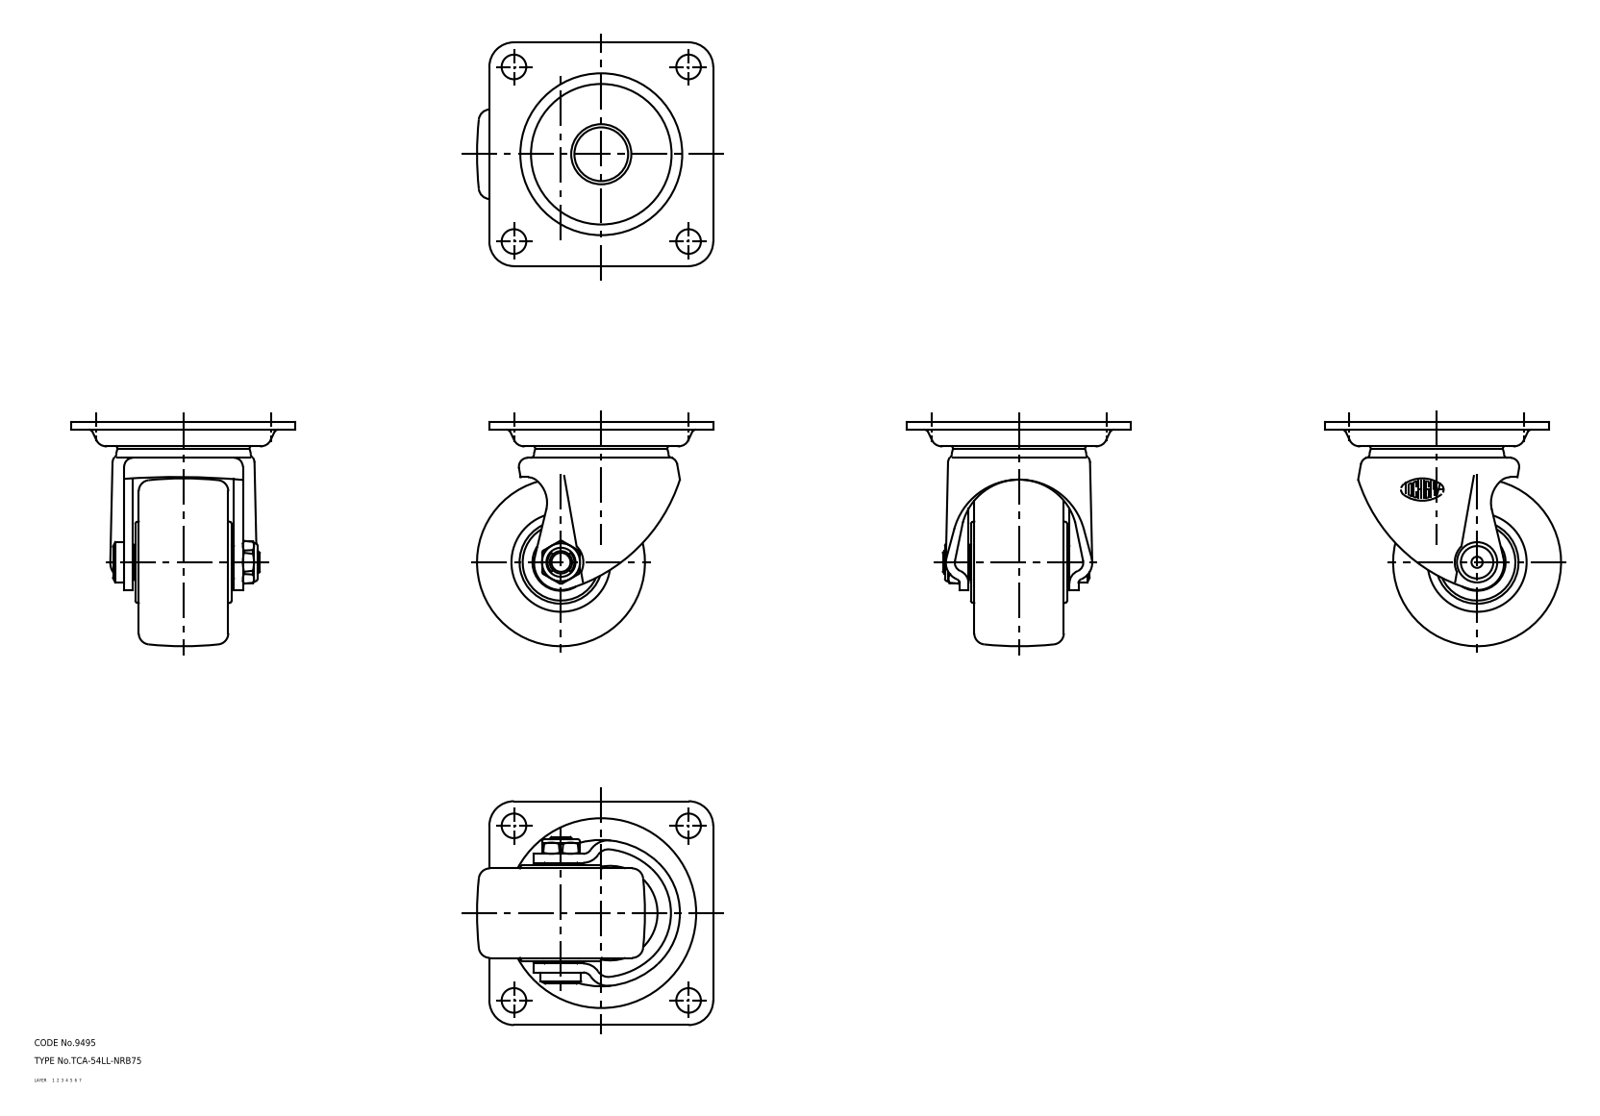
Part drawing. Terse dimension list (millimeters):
name: seal; nut; main shaft; wheel (+3 more)
written by: CADfix (AUTOMOTIVE_DESIGN)
unit: mm
bodies: 7 solids, 241 faces (0 planar, 0 cylindrical, 241 other)
size: 105.5 × 100 × 100
volume: 286 103 mm³; area: 75 879 mm²
